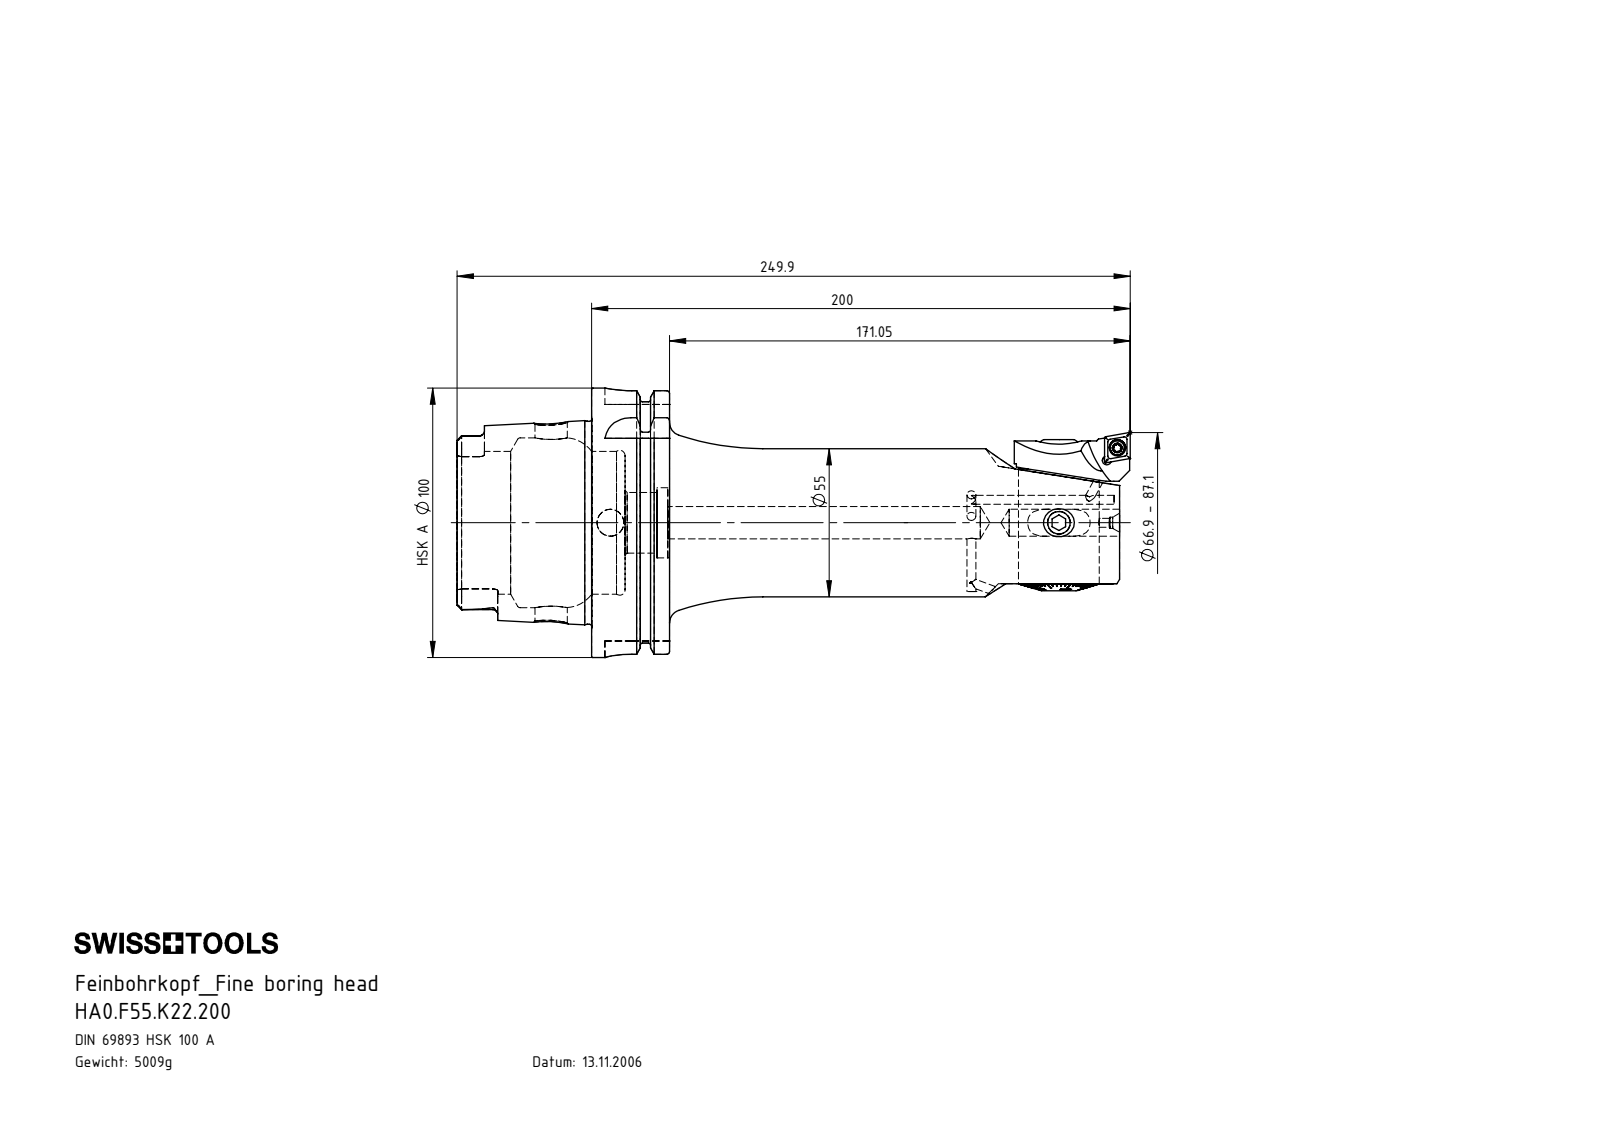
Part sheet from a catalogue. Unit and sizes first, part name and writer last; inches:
Units: inches
Overall size (bounding box): 9.839 × 3.937 × 3.937
Round holes (diameter × count): ⌀0.13 ×9, ⌀0.472 ×3, ⌀0.335 ×2, ⌀0.394 ×2, ⌀0.165 ×1, ⌀0.173 ×1, ⌀0.197 ×1, ⌀0.24 ×1, ⌀0.315 ×1, ⌀0.433 ×1, ⌀0.463 ×1, ⌀0.488 ×1
Round bosses / shafts (diameter × count): ⌀0.394 ×2, ⌀0.207 ×2, ⌀0.157 ×2, ⌀3.937 ×1, ⌀3.62 ×1, ⌀2.963 ×1, ⌀2.165 ×1, ⌀1.18 ×1
Partial cylindrical surfaces — rounded edges, fillets, slot ends (radius × count): R0.013 ×12, R0.023 ×12, R0.075 ×6, R0.394 ×6, R0.02 ×4, R0.192 ×4, R0.126 ×3, R0.039 ×1
Main face-to-face distances: 1.14, 0.49, 0.65, 7.717, 7.226, 6.577, 1.965, 2.455, 3.104, 9.681
Hole centre spacings: 0.226, 0.231, 0.383, 0.571, 0.827, 1.28, 6.142, 6.555
Volume: 38.97 in³ · Surface area: 164.3 in²
Bodies: 16 solids, 954 faces (366 planar, 207 cylindrical, 381 other)
Part name (STEP PRODUCT): F55-ER1.101.016_A; F55-WCB.001.013; F55-BG1.011.036_D; HA0.F55.K22.200 (+8 more)
STEP written by: SolidWorks 2022 (AUTOMOTIVE_DESIGN)
